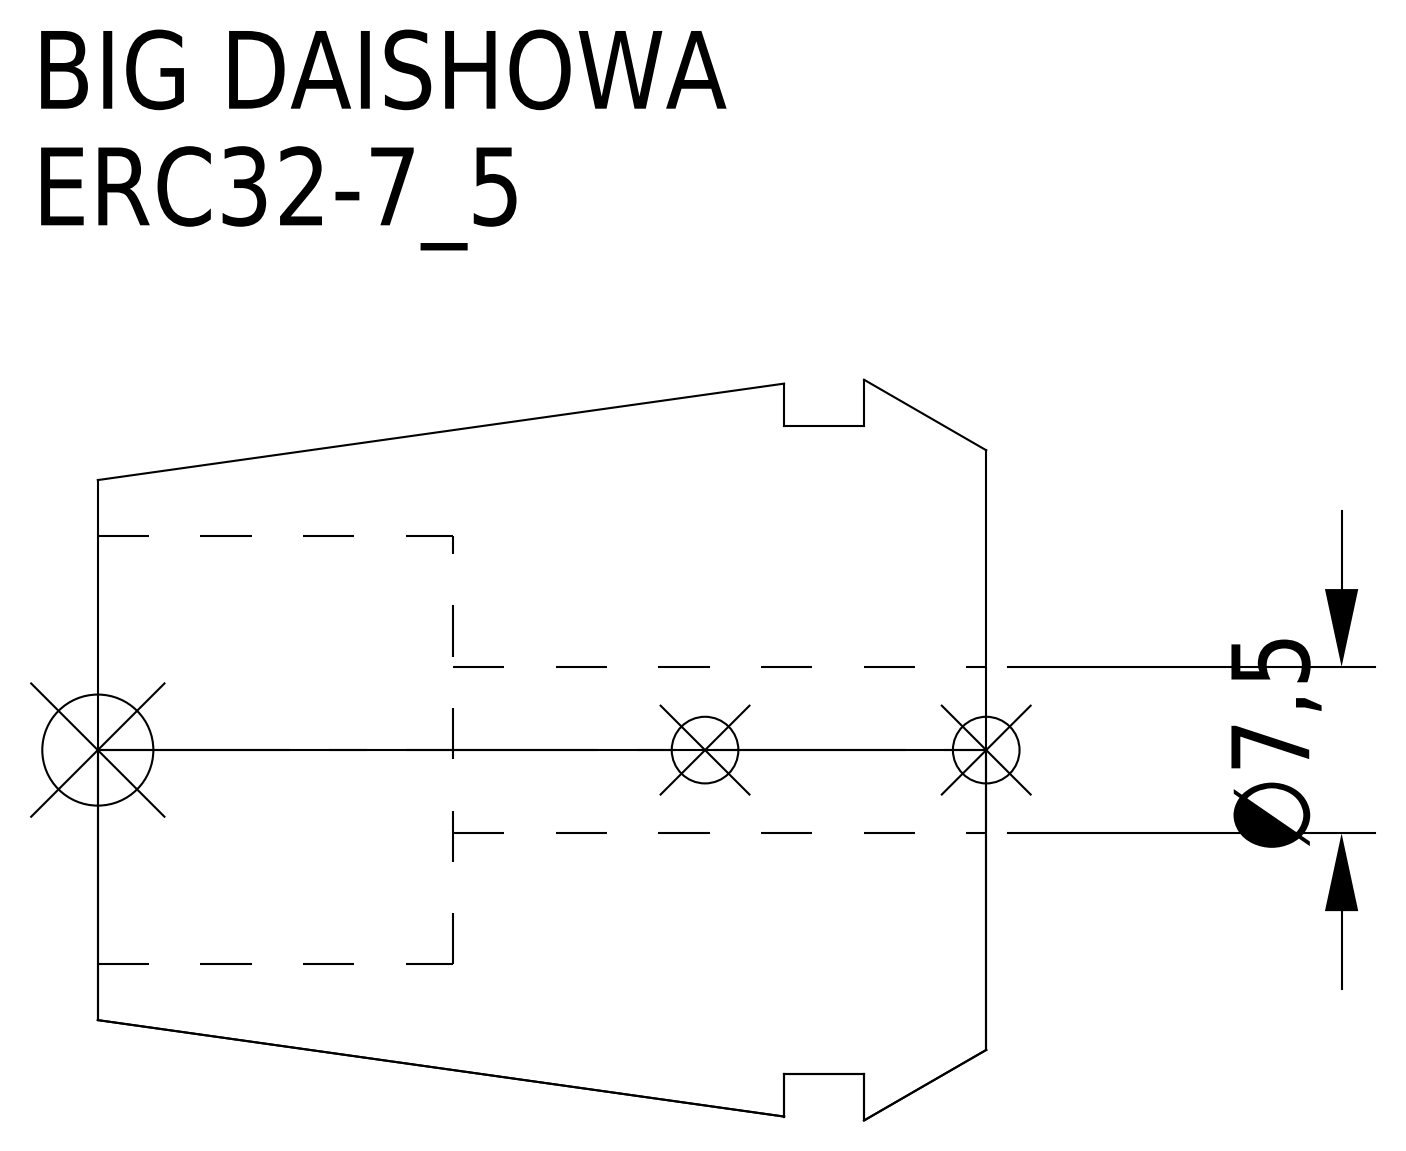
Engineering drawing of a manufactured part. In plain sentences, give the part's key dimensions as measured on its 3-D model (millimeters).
The part is named "ERC32-7_5". Its 3-D file was written by "CREO PARAMETRIC BY PTC INC, 2016380 (AUTOMOTIVE_DESIGN)". It is 1 solid with 15 faces: 5 planar, 6 cylindrical and 4 other. Overall it measures 40 by 33.35 by 33.35 millimeters. Its volume is 20 701 cubic millimeters and its surface area 6 615 square millimeters. Round holes: 1 of diameter 7.5, 1 of diameter 19.3. Round bosses or shafts: 1 of diameter 29.2. The main face-to-face distances are 24, 5.5, 18.5, 9.1, 3.6, 14.9, 40, 34.5, 30.9, 16.
